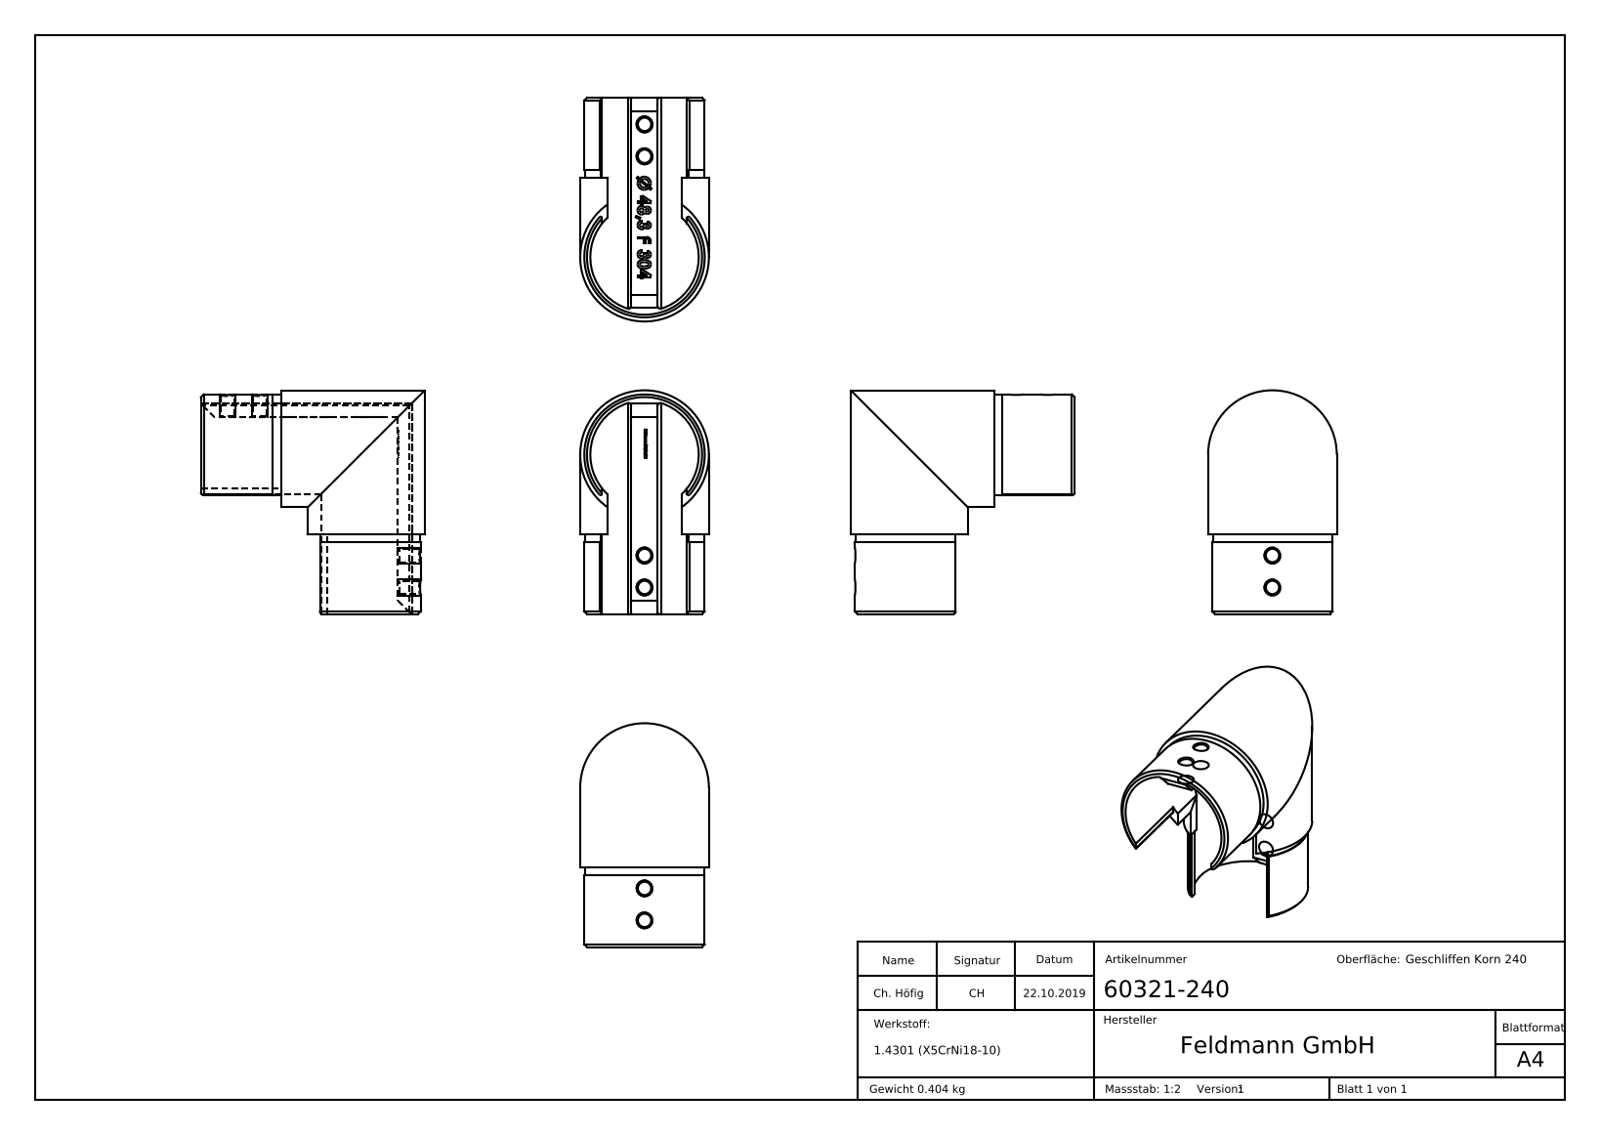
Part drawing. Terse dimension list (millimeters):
name: 60321-240
written by: SolidWorks 2015 (CONFIG_CONTROL_DESIGN)
unit: mm
bodies: 1 solid, 410 faces (211 planar, 22 cylindrical, 177 other)
size: 84 × 84 × 48.3
volume: 51 065 mm³; area: 30 382 mm²
holes: 4× ⌀5
bosses: 2× ⌀48.3
rounds: 4× R0.5, 4× R1, 2× R20.35, 2× R22.4, 2× R22.6
face distances: 10, 30, 43.95, 73.95, 11, 21, 2, 9, 19, 32
hole spacings: 12
